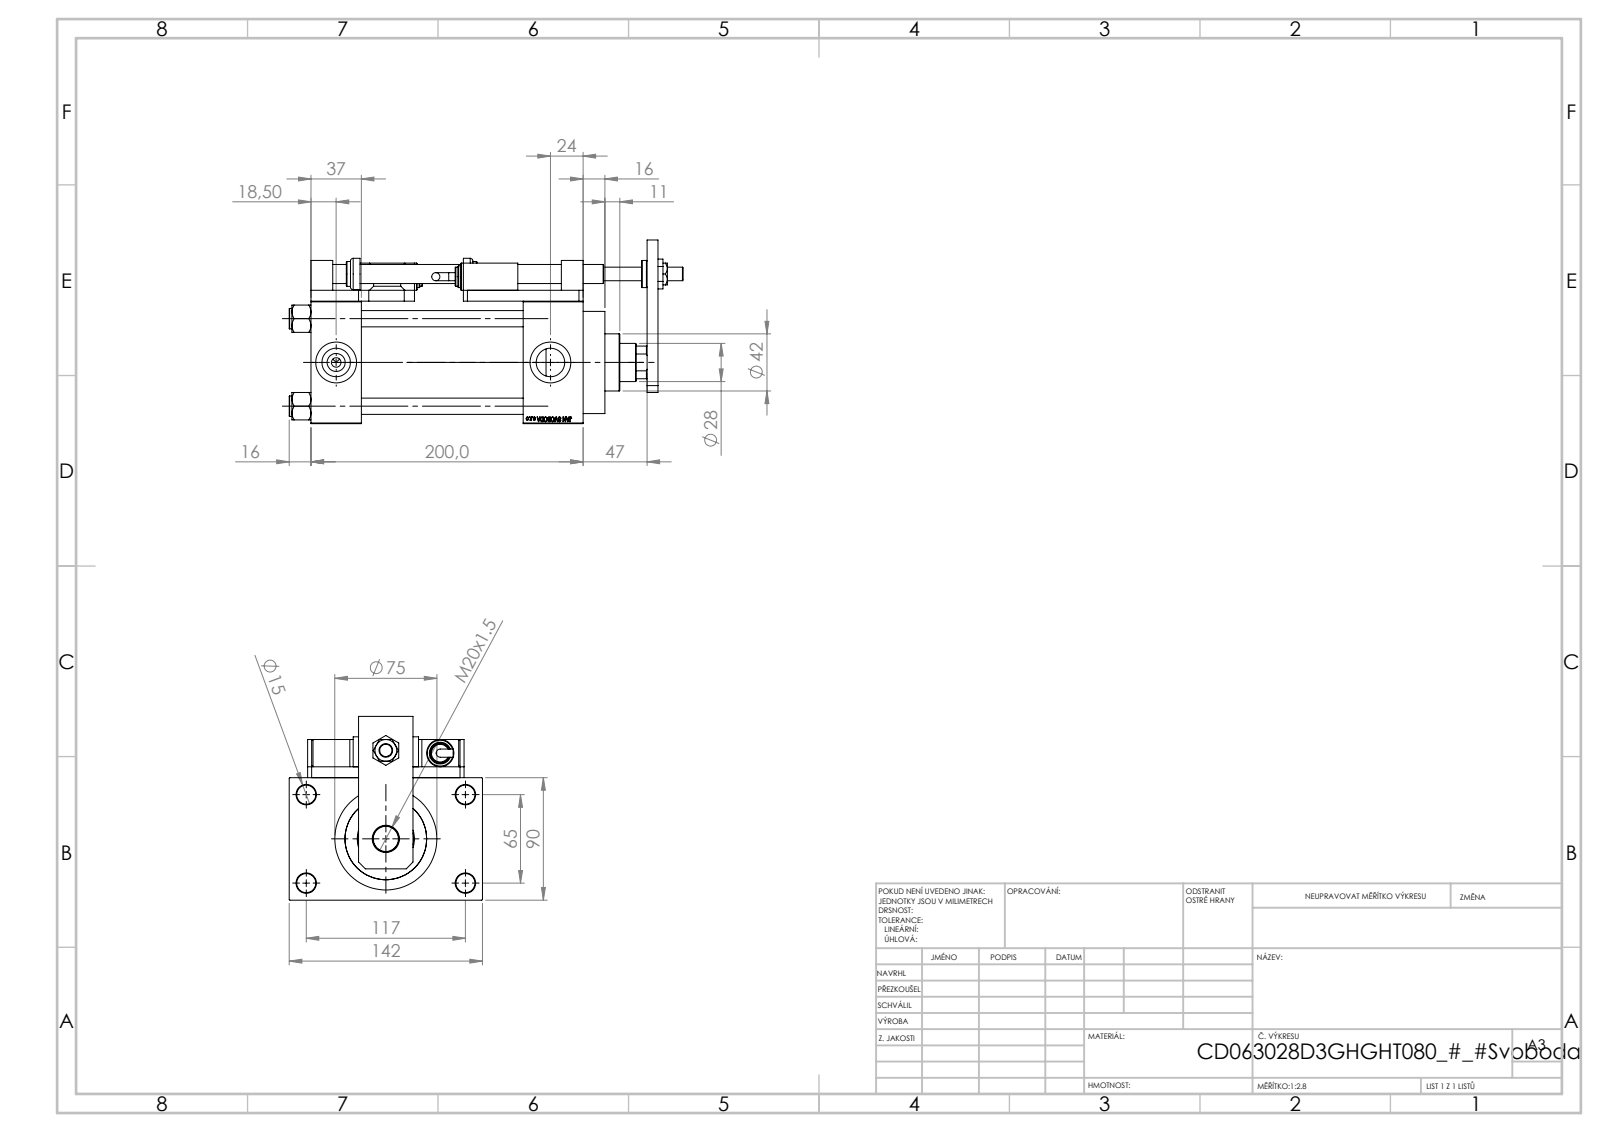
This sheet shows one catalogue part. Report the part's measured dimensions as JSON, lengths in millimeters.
{"part_name": "V215CD_SWITCH_Q_NUT10; V215CD_SWITCH_Q_BLOK; V215CD_VCP_D; V215CD_NUT_M5_D (+7 more)", "step_written_by": "SolidWorks 2019 (CONFIG_CONTROL_DESIGN)", "units": "millimeters", "bodies": {"solids": 26, "faces": 1432, "planar": 666, "cylindrical": 167, "other": 599}, "overall_size": [289.5, 142, 135], "volume_mm3": 1467000, "surface_area_mm2": 332028, "round_holes": [[14, 5], [8.5, 4], [12, 4], [13.5, 4], [20.96, 4], [30, 4], [7, 3], [10, 1], [18.5, 1], [20, 1], [28, 1], [31, 1]], "round_bosses_or_shafts": [[15, 4], [20, 3], [16, 2], [14, 2], [6, 2], [75, 1], [69, 1], [42, 1]], "partial_cylinders_radius": [[7.5, 4], [13.5, 1]], "face_to_face_distances": [8, 90, 44, 200, 37, 98, 163, 156, 119, 47], "hole_center_spacings": [66.92, 26.35, 45.47, 64.3, 69.81, 90.65, 111.34, 65]}
